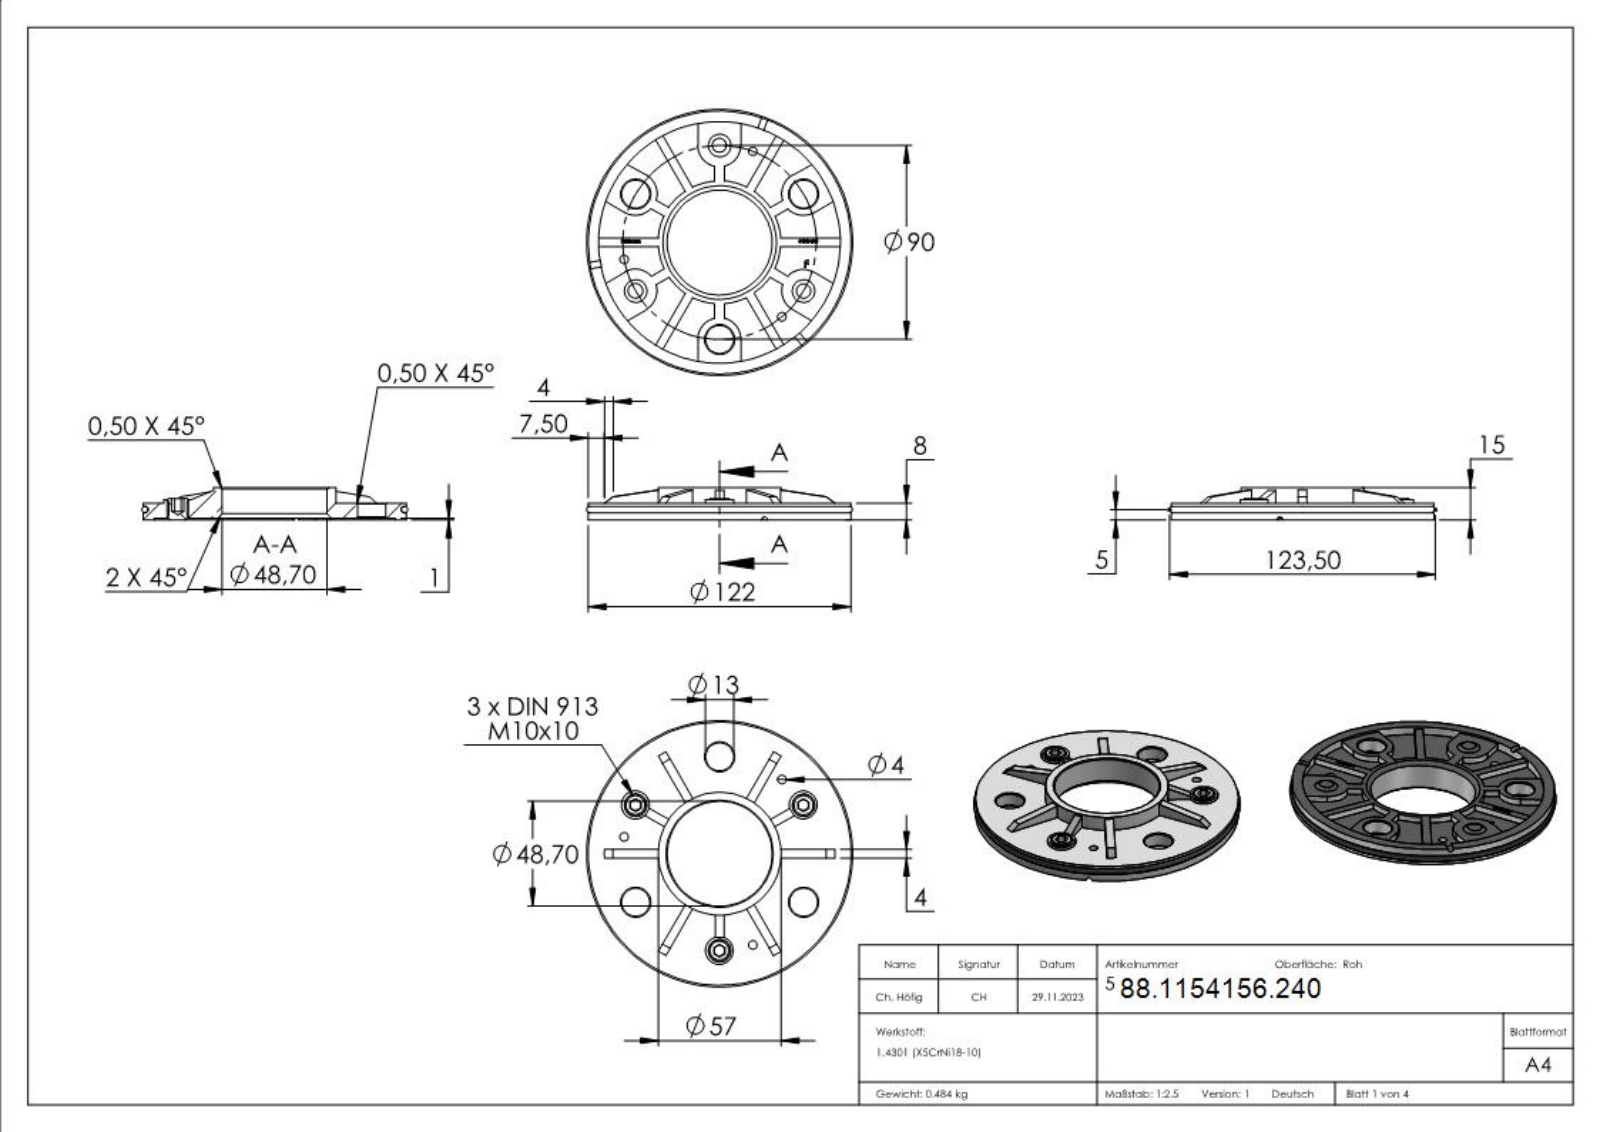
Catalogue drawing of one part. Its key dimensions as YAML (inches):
part_name: "DIN913_DIN 913 M10x10; 5415X-240 Teil2_54156-240 Teil2; 54156-240; 5415X-XXX Teil1_54156-240 Teil1"
step_written_by: "SolidWorks 2018 (CONFIG_CONTROL_DESIGN)"
units: inches
bodies: {solids: 5, faces: 442, planar: 268, cylindrical: 47, other: 127}
overall_size: [4.862, 4.862, 0.591]
volume: 3.881
surface_area: 58.02
round_holes:
  - {diameter: 0.157, count: 3}
  - {diameter: 0.335, count: 3}
  - {diameter: 0.512, count: 3}
  - {diameter: 1.917, count: 1}
  - {diameter: 4.409, count: 1}
round_bosses_or_shafts:
  - {diameter: 0.512, count: 3}
  - {diameter: 0.394, count: 3}
  - {diameter: 4.803, count: 1}
  - {diameter: 2.244, count: 1}
partial_cylinders:
  - {radius: 0.394, count: 6}
  - {radius: 0.059, count: 3}
face_to_face_distances: [0.157, 0.276, 0.118, 0.315, 0.039, 0.591, 0.551, 0.433, 0.098, 0.217]
hole_center_spacings: [1.772, 3.069, 3.543, 0.615, 1.212, 2.278, 2.715, 3.069]
